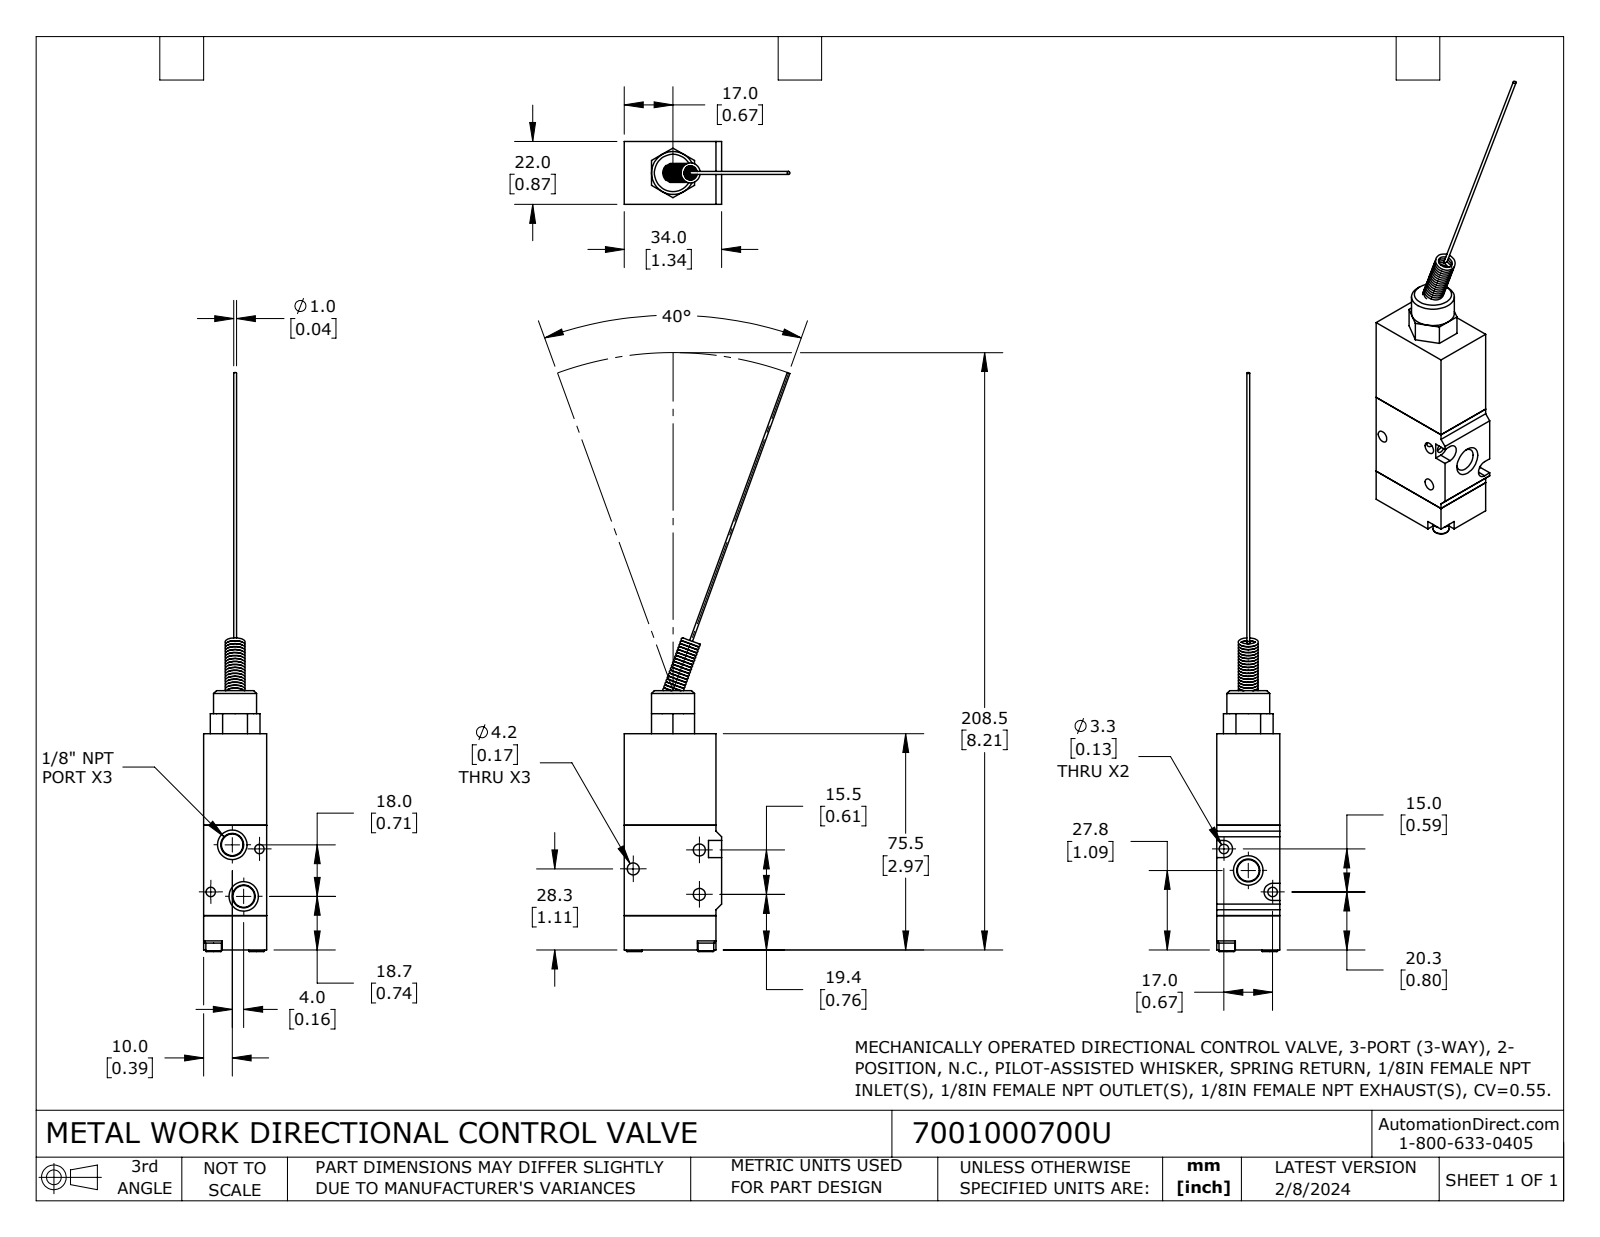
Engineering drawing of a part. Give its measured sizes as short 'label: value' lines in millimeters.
name: 7001000700U
written by: SolidWorks 2023 (CONFIG_CONTROL_DESIGN)
unit: mm
bodies: 8 solids, 376 faces (85 planar, 120 cylindrical, 171 other)
size: 202.2 × 57.8 × 22
volume: 54 670 mm³; area: 17 260 mm²
holes: 3× ⌀4.2, 2× ⌀3, 2× ⌀3.3, 1× ⌀6
bosses: 2× ⌀6, 2× ⌀5.5, 2× ⌀1, 1× ⌀15, 1× ⌀6
rounds: 2× R3
face distances: 22, 32, 31.5, 12, 43.5, 75.5, 63.5, 2, 34, 15
hole spacings: 15.5, 22.7, 24, 24.8, 29.2
